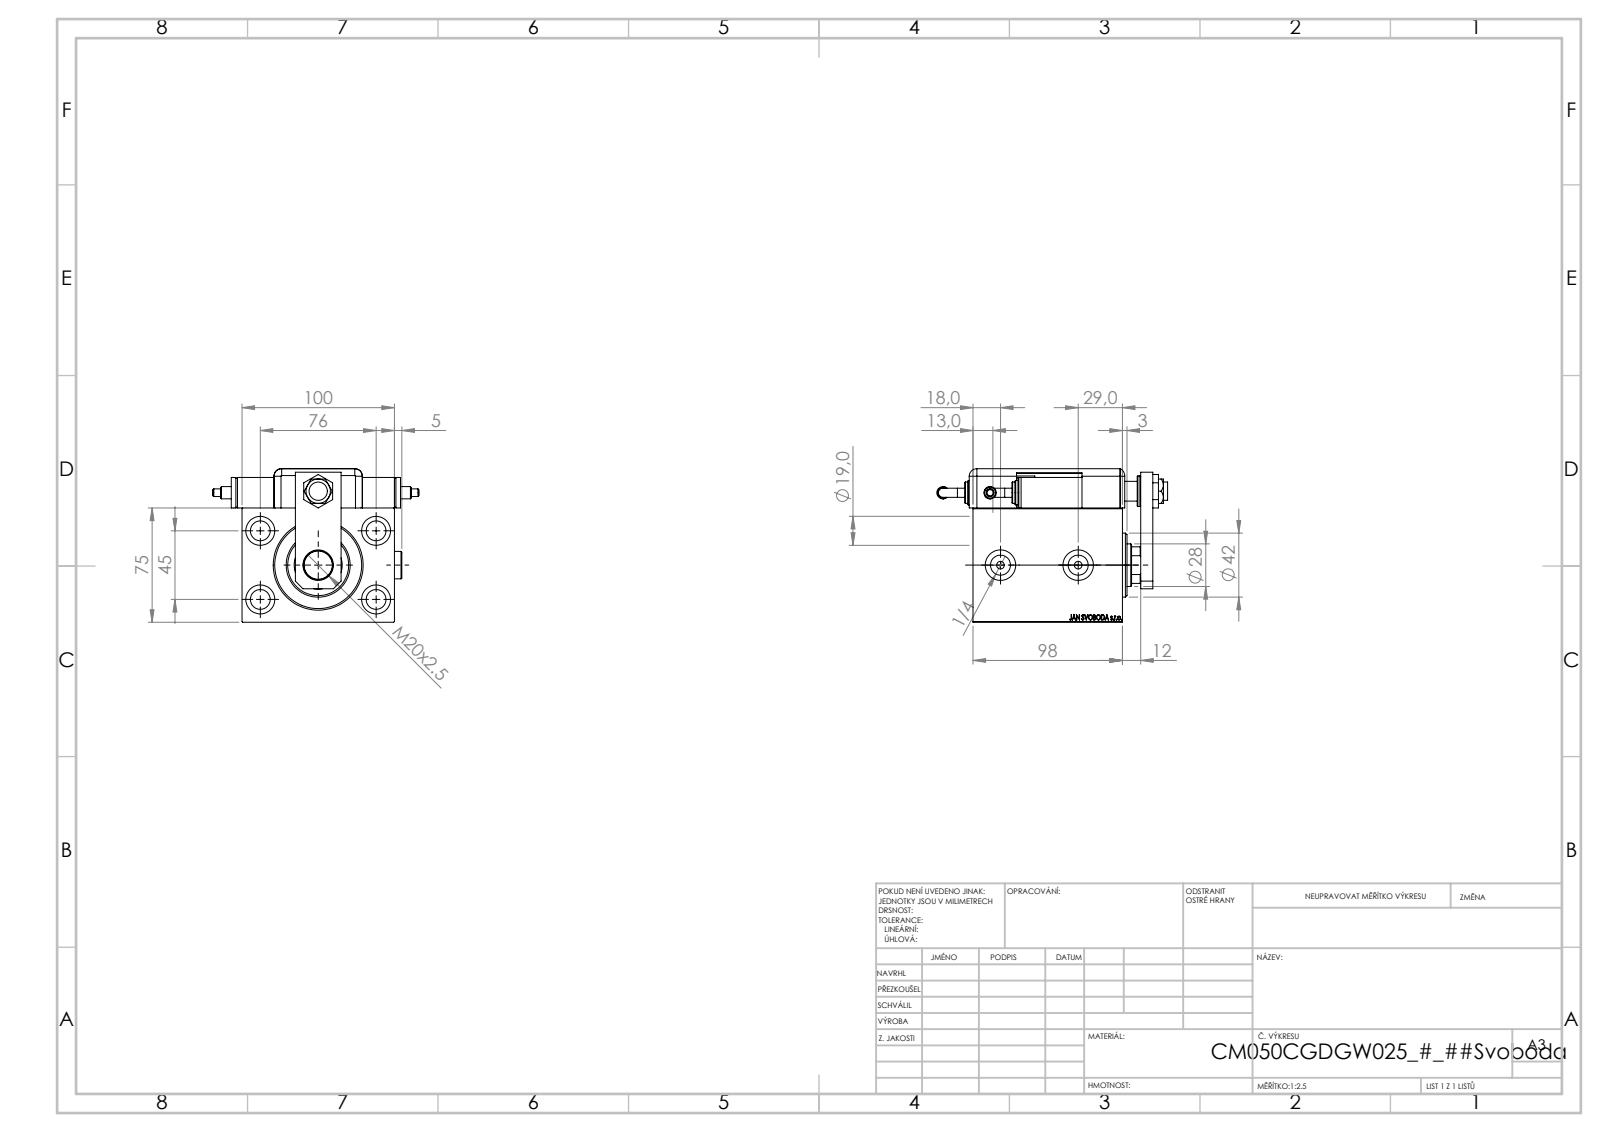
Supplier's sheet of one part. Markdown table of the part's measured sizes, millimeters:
| quantity | value |
| --- | --- |
| part name | Zatka_OIL_PORT; NUT_D19; SWITCH_Q_FRONT_BACK; TYC (+7 more) |
| STEP written by | SolidWorks 2019 (CONFIG_CONTROL_DESIGN) |
| units | millimeters |
| bodies | 15 solids, 1331 faces (653 planar, 141 cylindrical, 537 other) |
| overall size | 151.46 × 135.01 × 100.8 |
| volume | 772 529 mm³ |
| surface area | 163 728 mm² |
| round holes (diameter × count) | 13 × 5, 19 × 4, 20 × 3, 4 × 2, 5 × 2, 8 × 2, 13.16 × 2, 12 × 1, 14 × 1, 18.5 × 1, 28 × 1, 31.5 × 1 |
| round bosses / shafts (diameter × count) | 20 × 3, 18 × 2, 16 × 2, 14 × 2, 8 × 2, 6 × 2, 5.04 × 2, 42 × 1 |
| partial cylindrical surfaces (radius × count) | 5 × 9, 10 × 1, 13.5 × 1 |
| main face-to-face distances | 75, 3, 100, 98, 14, 20, 13.5, 84, 25.8, 100.8 |
| hole center spacings | 44.16, 45, 46.04, 76, 80.53, 88.32, 20, 48.5 |
